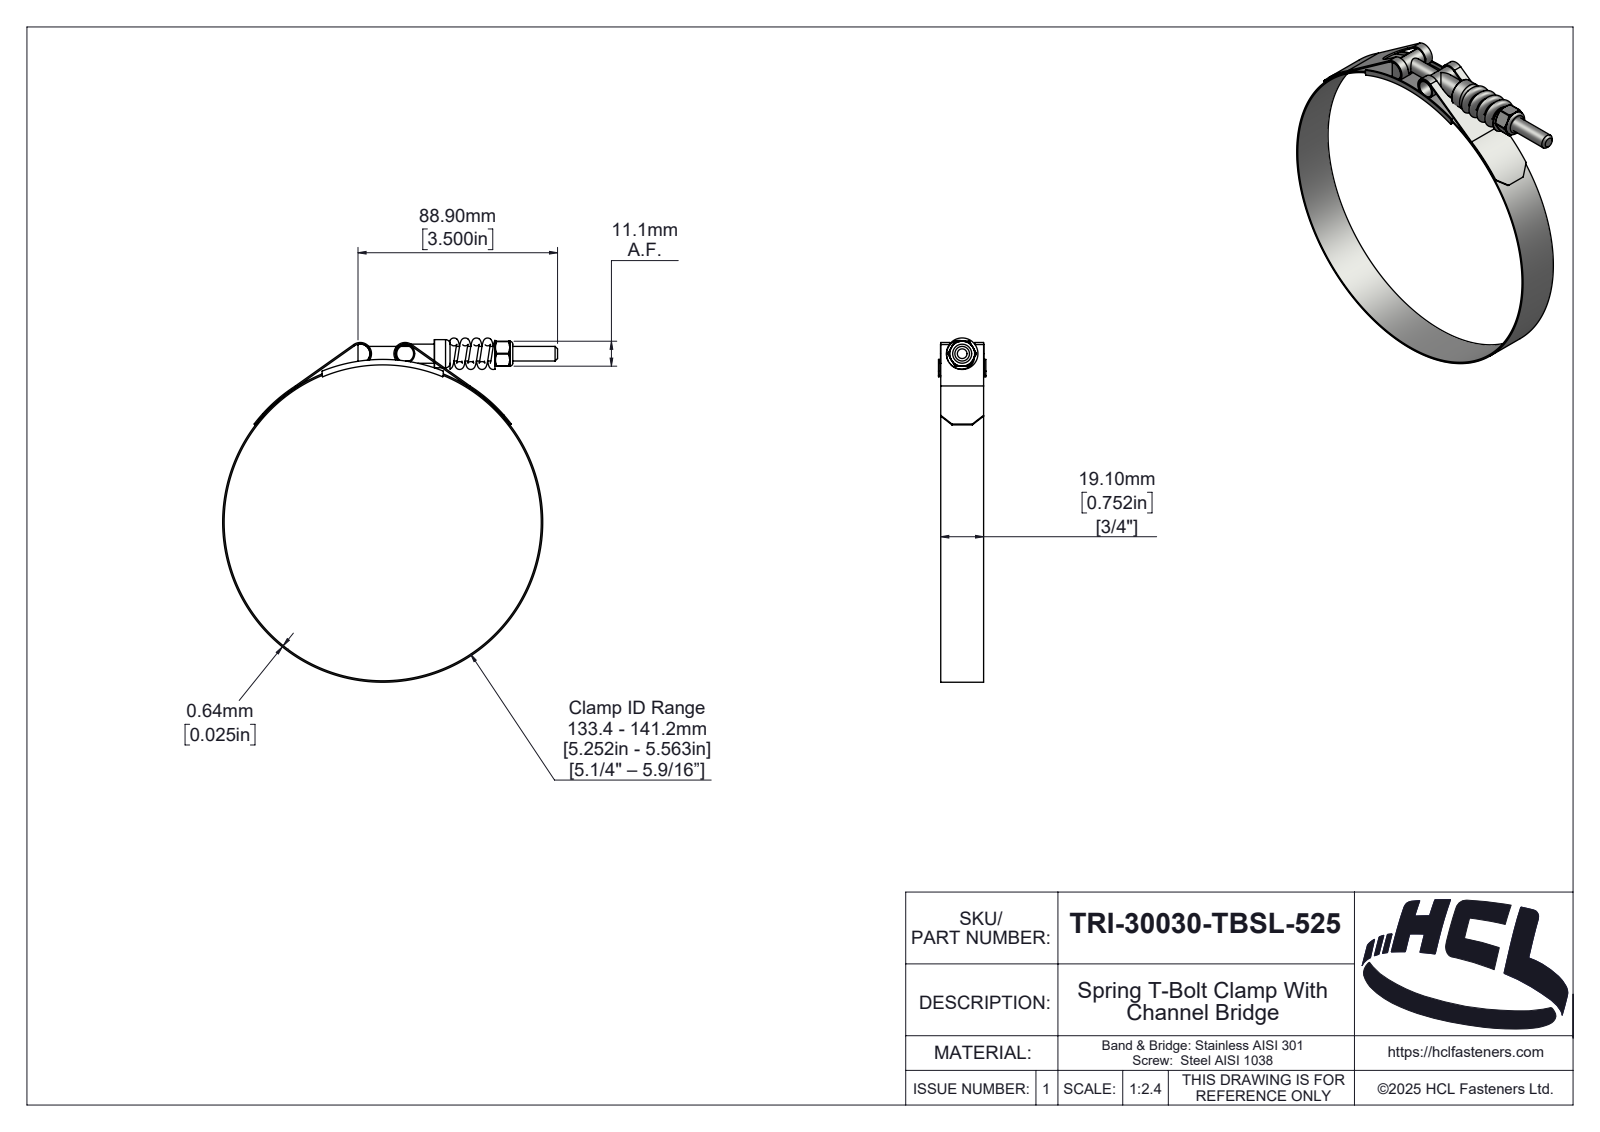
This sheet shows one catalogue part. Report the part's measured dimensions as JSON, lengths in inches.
{"part_name": "TRI-30030-TBSL-525", "step_written_by": "SolidWorks 2025 (AUTOMOTIVE_DESIGN)", "units": "inches", "bodies": {"solids": 7, "faces": 332, "planar": 48, "cylindrical": 122, "other": 162}, "overall_size": [6.035, 5.913, 0.831], "volume_in3": 0.851, "surface_area_in2": 48, "round_holes": [[0.213, 1], [0.25, 1], [0.256, 1], [0.296, 1], [5.563, 1]], "round_bosses_or_shafts": [[0.335, 2], [5.613, 1], [0.493, 1]], "partial_cylinders_radius": [[0.015, 6], [0.02, 2], [0.172, 2], [0.197, 2], [0.023, 1], [0.095, 1], [0.119, 1], [0.126, 1]], "face_to_face_distances": [0.025, 0.752, 0.039, 0.791, 0.806, 0.014, 0.766, 0.831, 2.402, 0.437], "hole_center_spacings": [2.978]}
